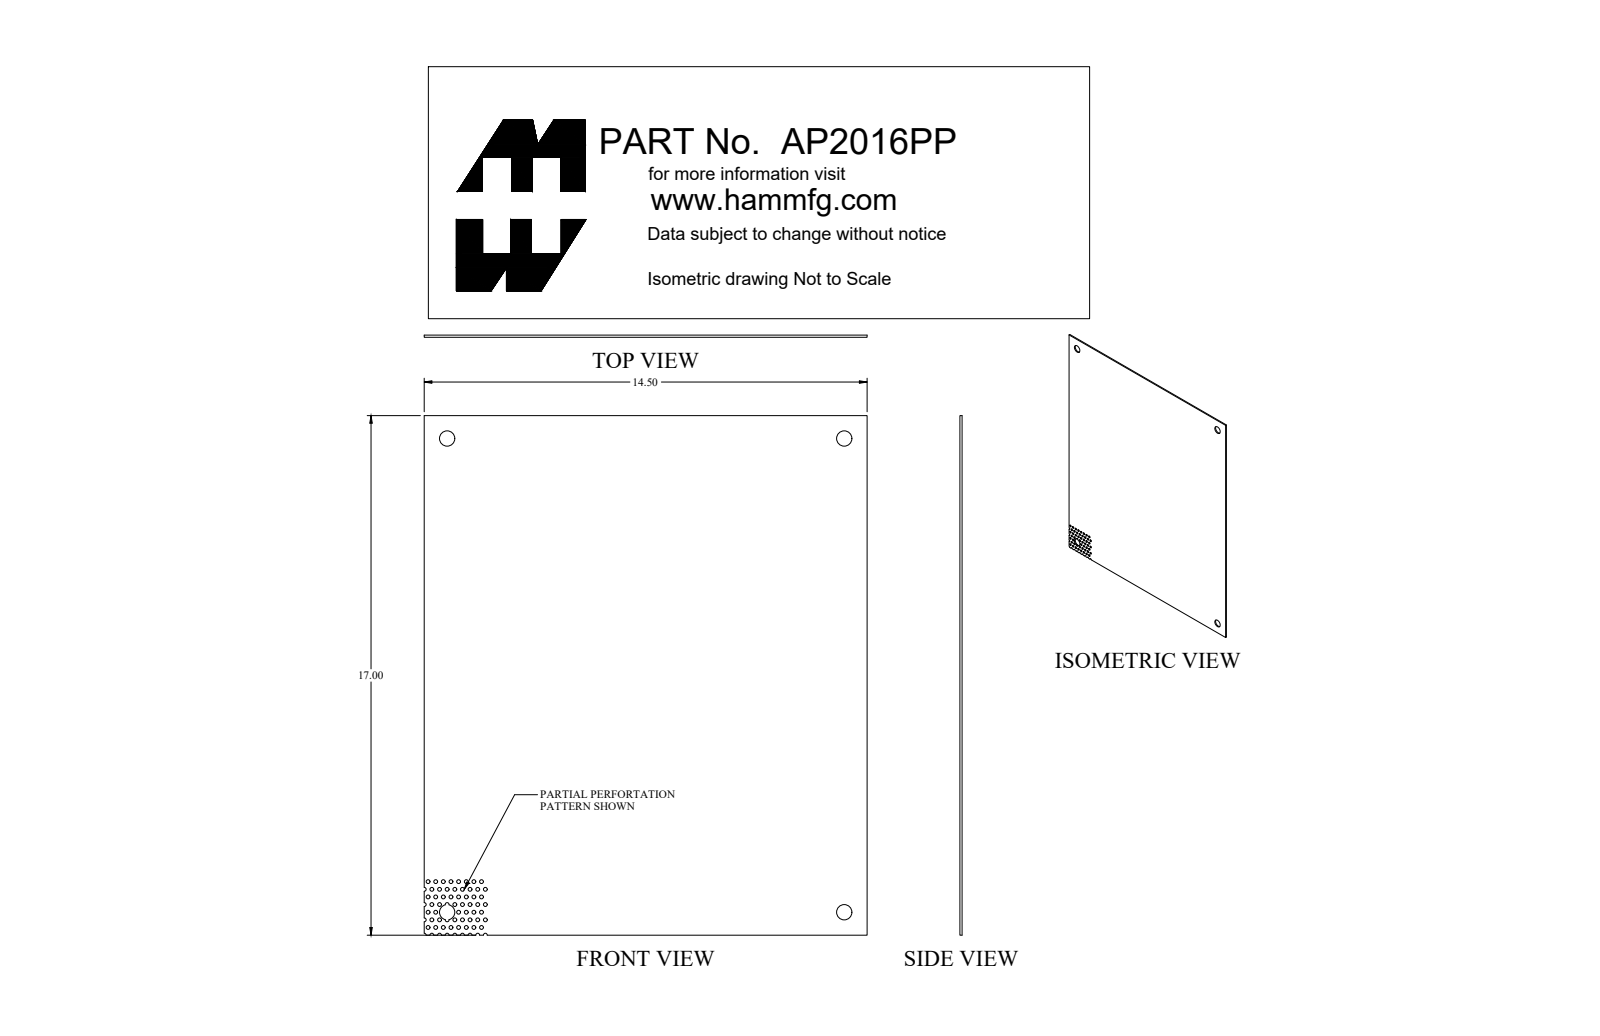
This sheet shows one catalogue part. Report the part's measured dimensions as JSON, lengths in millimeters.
{"part_name": "AP2016PP_Default", "step_written_by": "SolidWorks 2019 (CONFIG_CONTROL_DESIGN)", "units": "millimeters", "bodies": {"solids": 1, "faces": 152, "planar": 17, "cylindrical": 135, "other": 0}, "overall_size": [431.8, 368.3, 1.8], "volume_mm3": 289100, "surface_area_mm2": 320300, "round_holes": [[3.2, 52], [12.7, 4]], "partial_cylinders_radius": [[1.6, 14]], "face_to_face_distances": [1.8, 368.3, 431.8], "hole_center_spacings": [7.1, 12.7, 6.4, 11.4, 14.2, 17.1, 29.3, 23.1]}
